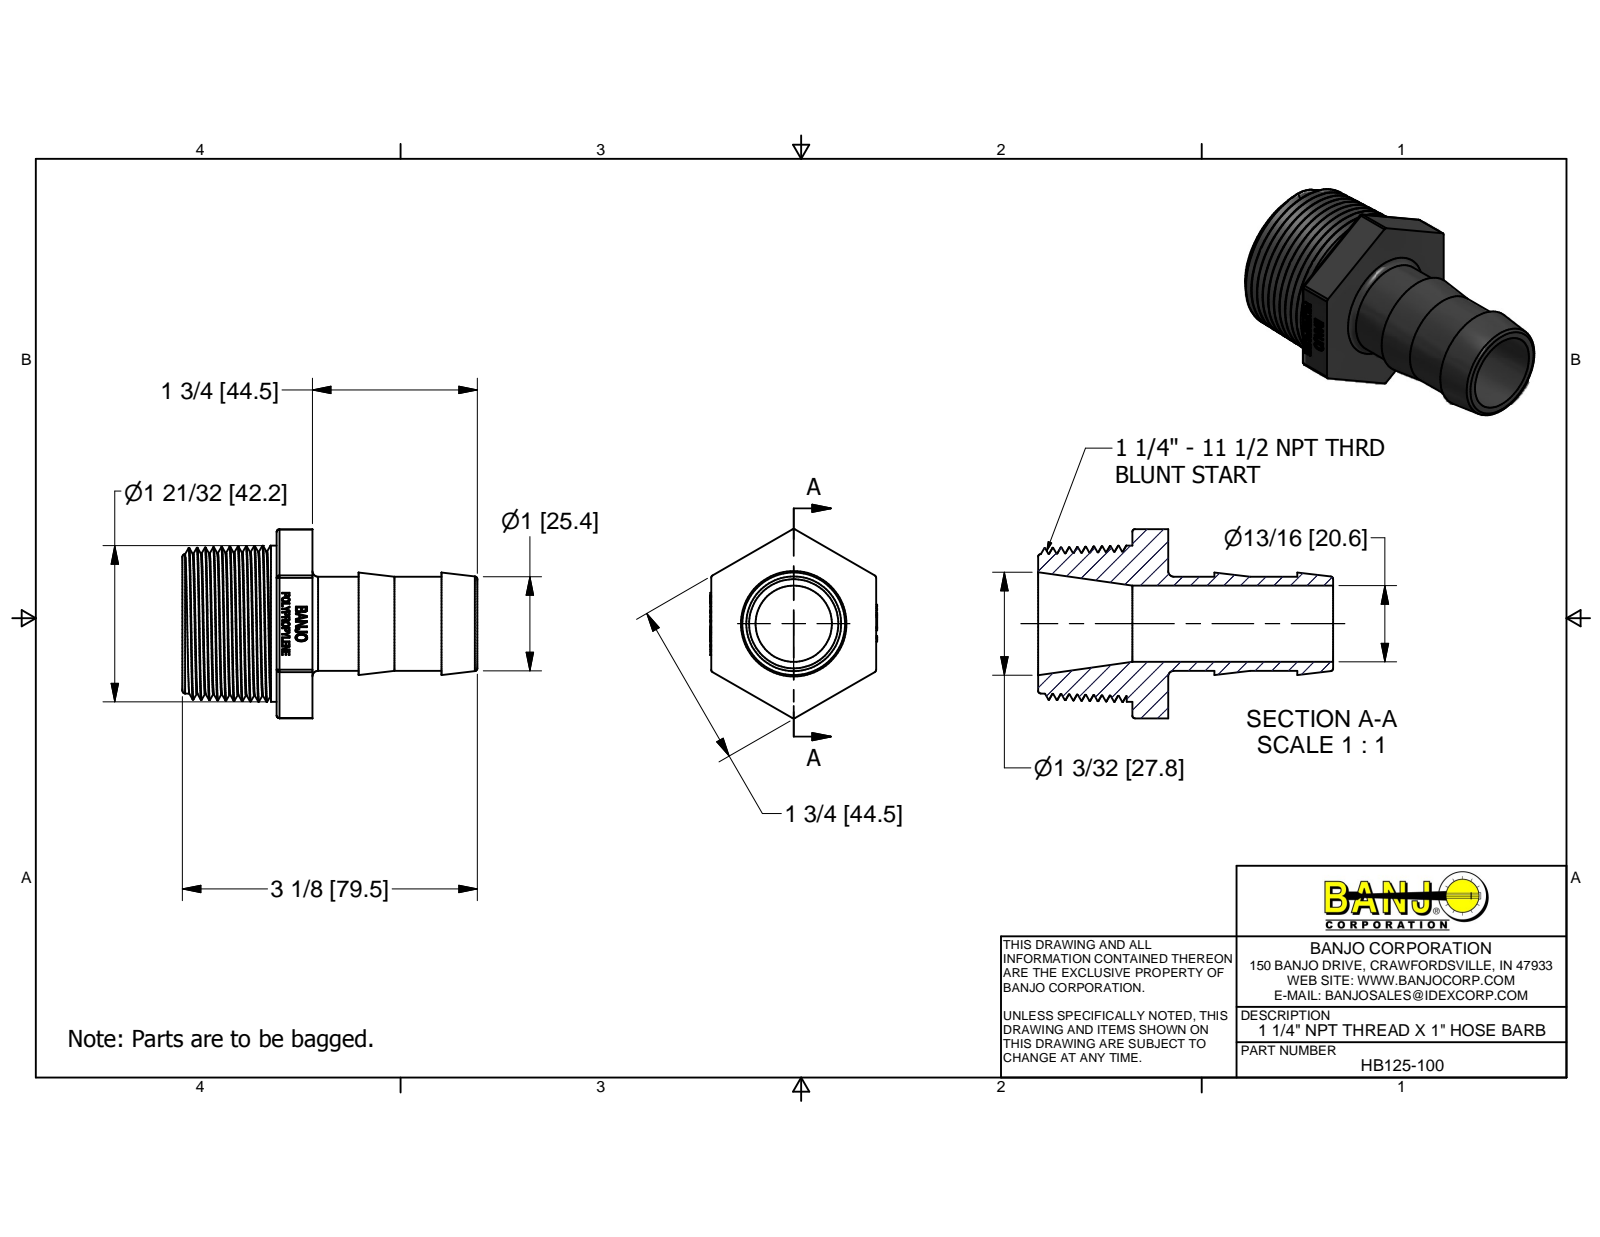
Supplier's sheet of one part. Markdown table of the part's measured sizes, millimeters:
| quantity | value |
| --- | --- |
| part name | HB125-100 |
| STEP written by | Autodesk Inventor 2014 (AUTOMOTIVE_DESIGN) |
| units | millimeters |
| bodies | 1 solid, 383 faces (242 planar, 20 cylindrical, 121 other) |
| overall size | 79.5 × 51.09 × 44.96 |
| volume | 42 045 mm³ |
| surface area | 18 434 mm² |
| round holes (diameter × count) | 20.57 × 1 |
| round bosses / shafts (diameter × count) | 42.16 × 1, 25.4 × 1 |
| partial cylindrical surfaces (radius × count) | 0.76 × 12, 11.02 × 1, 12.95 × 1 |
| main face-to-face distances | 44.44, 35.05, 9.65, 44.45, 25.4, 79.5, 54.1, 23.88, 1.52, 11.17 |
